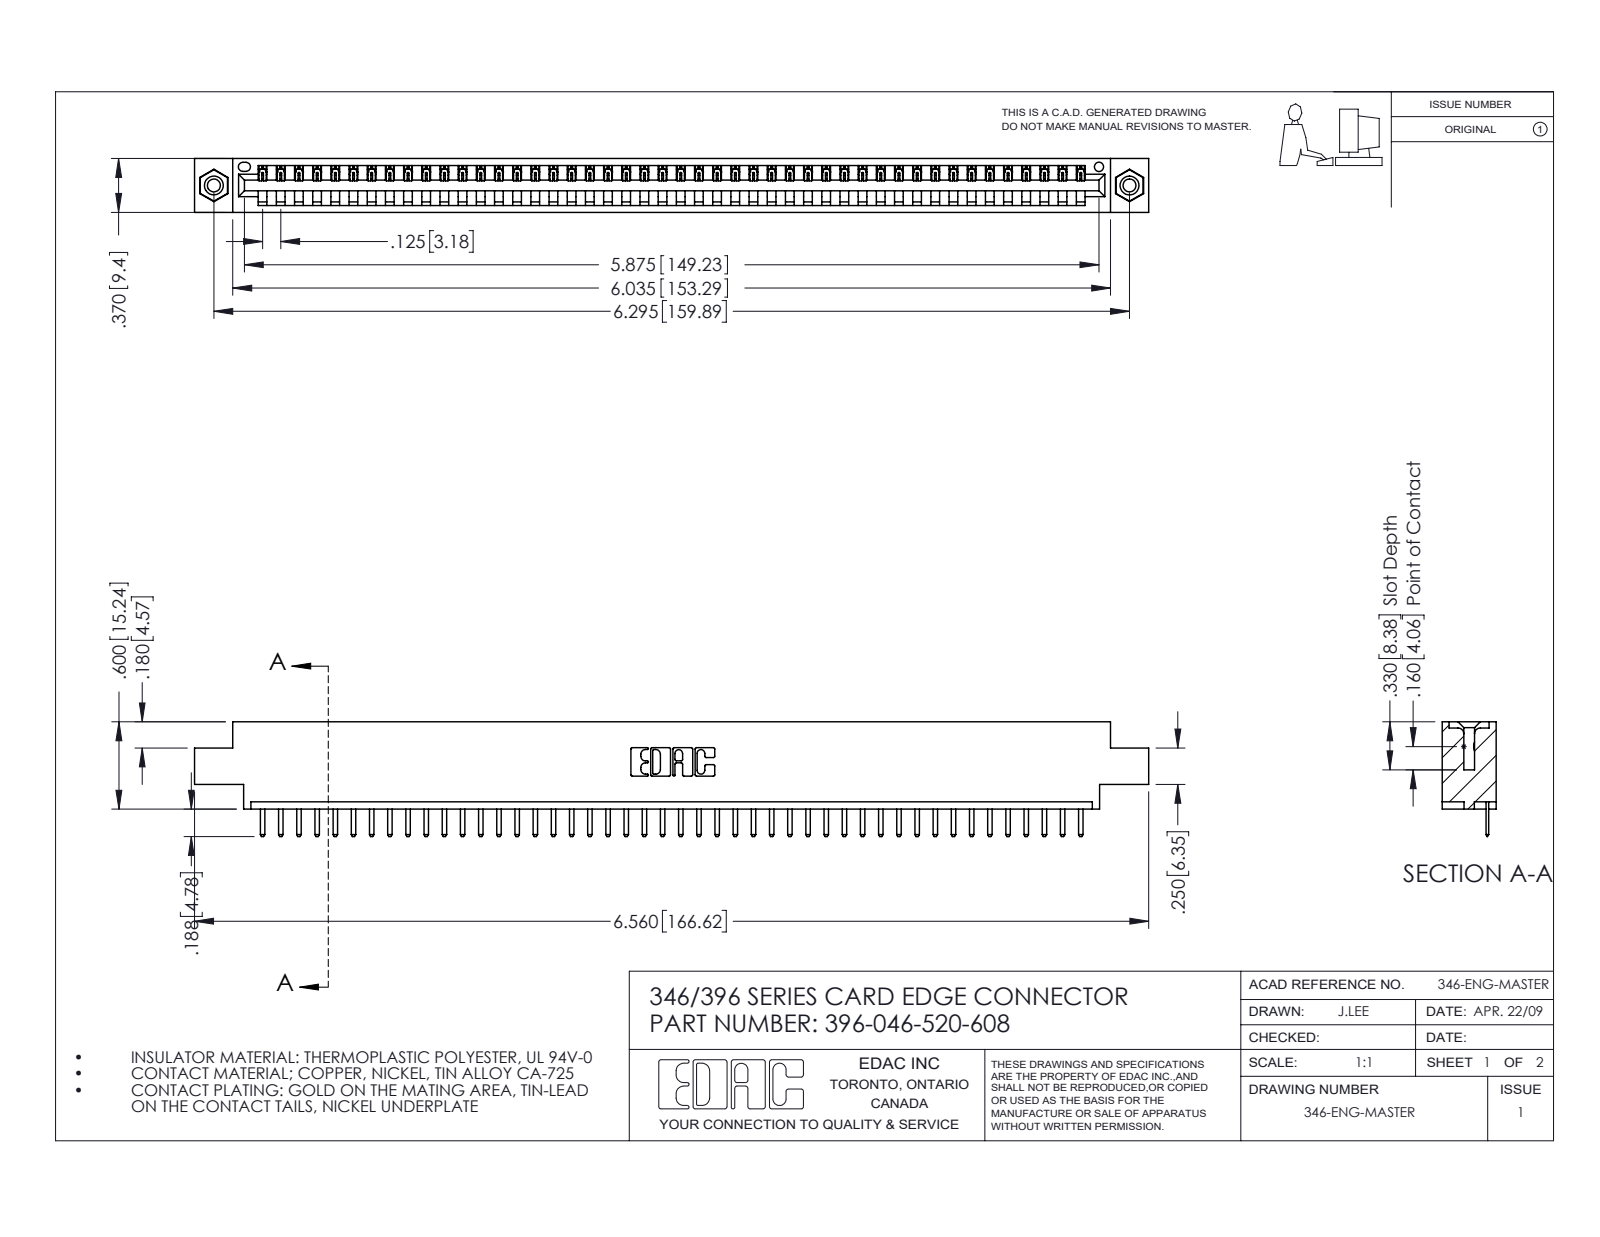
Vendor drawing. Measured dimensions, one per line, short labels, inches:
name: 396-046-520-608; 345-250-001_345-250-003-102; 346 Part_0.170 Offset - 0.156 Dia-TI; 345-292-001_345-293-120
written by: SolidWorks 2016 (CONFIG_CONTROL_DESIGN)
unit: in
bodies: 49 solids, 3038 faces (2044 planar, 978 cylindrical, 16 other)
size: 6.56 × 0.788 × 0.37
volume: 0.957 in³; area: 30.05 in²
holes: 2× ⌀0.089, 2× ⌀0.125, 2× ⌀0.156, 1× ⌀0.064
bosses: 2× ⌀0.155
rounds: 94× R0.01, 92× R0.006, 22× R0.01, 6× R0.007, 6× R0.031, 3× R0.026, 2× R0.031, 2× R0.04
face distances: 0.048, 0.322, 0.37, 0.25, 0.222, 0.148, 0.1, 0.174, 0.072, 0.298
hole spacings: 0.246, 6.086, 6.295
